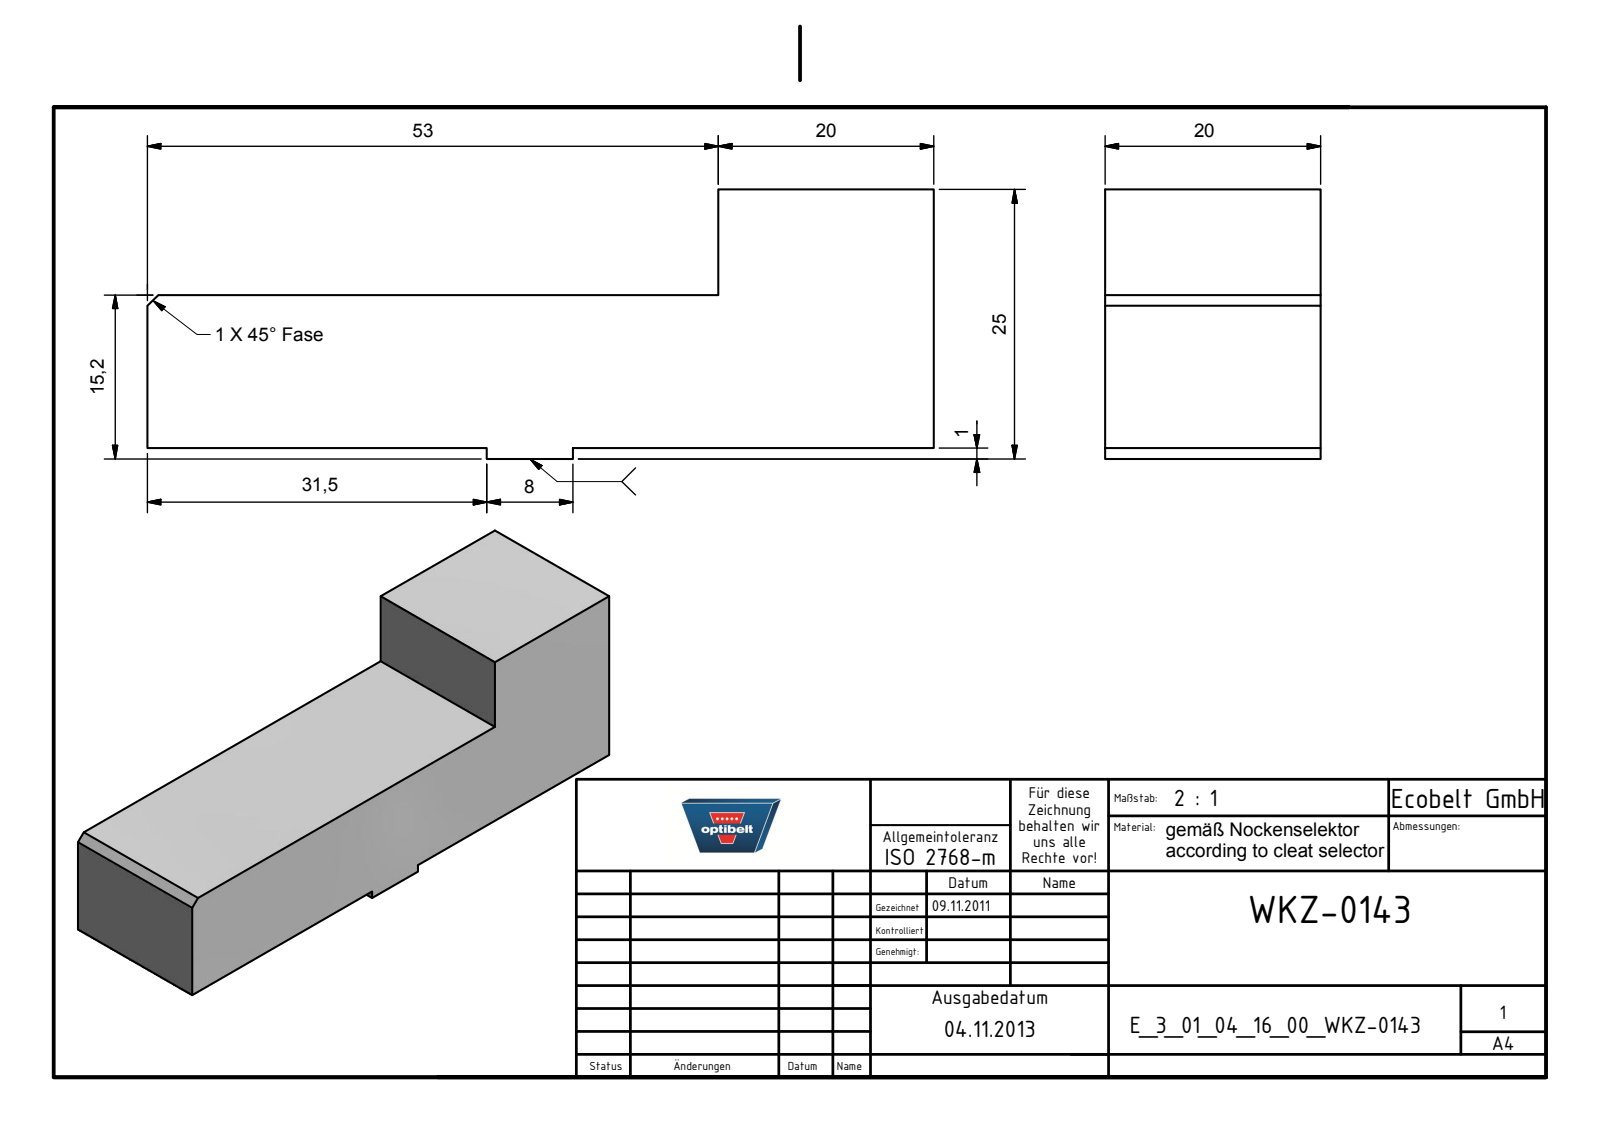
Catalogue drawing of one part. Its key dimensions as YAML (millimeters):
part_name: "E_3_01_04_16_00_WKZ-0143"
step_written_by: "Autodesk Inventor 2025 (AUTOMOTIVE_DESIGN)"
units: millimeters
bodies: {solids: 1, faces: 13, planar: 13, cylindrical: 0, other: 0}
overall_size: [73, 25, 20]
volume: 24802
surface_area: 6388
face_to_face_distances: [20, 14.2, 24, 9.8, 73, 53, 1, 15.2, 25, 31.5]
